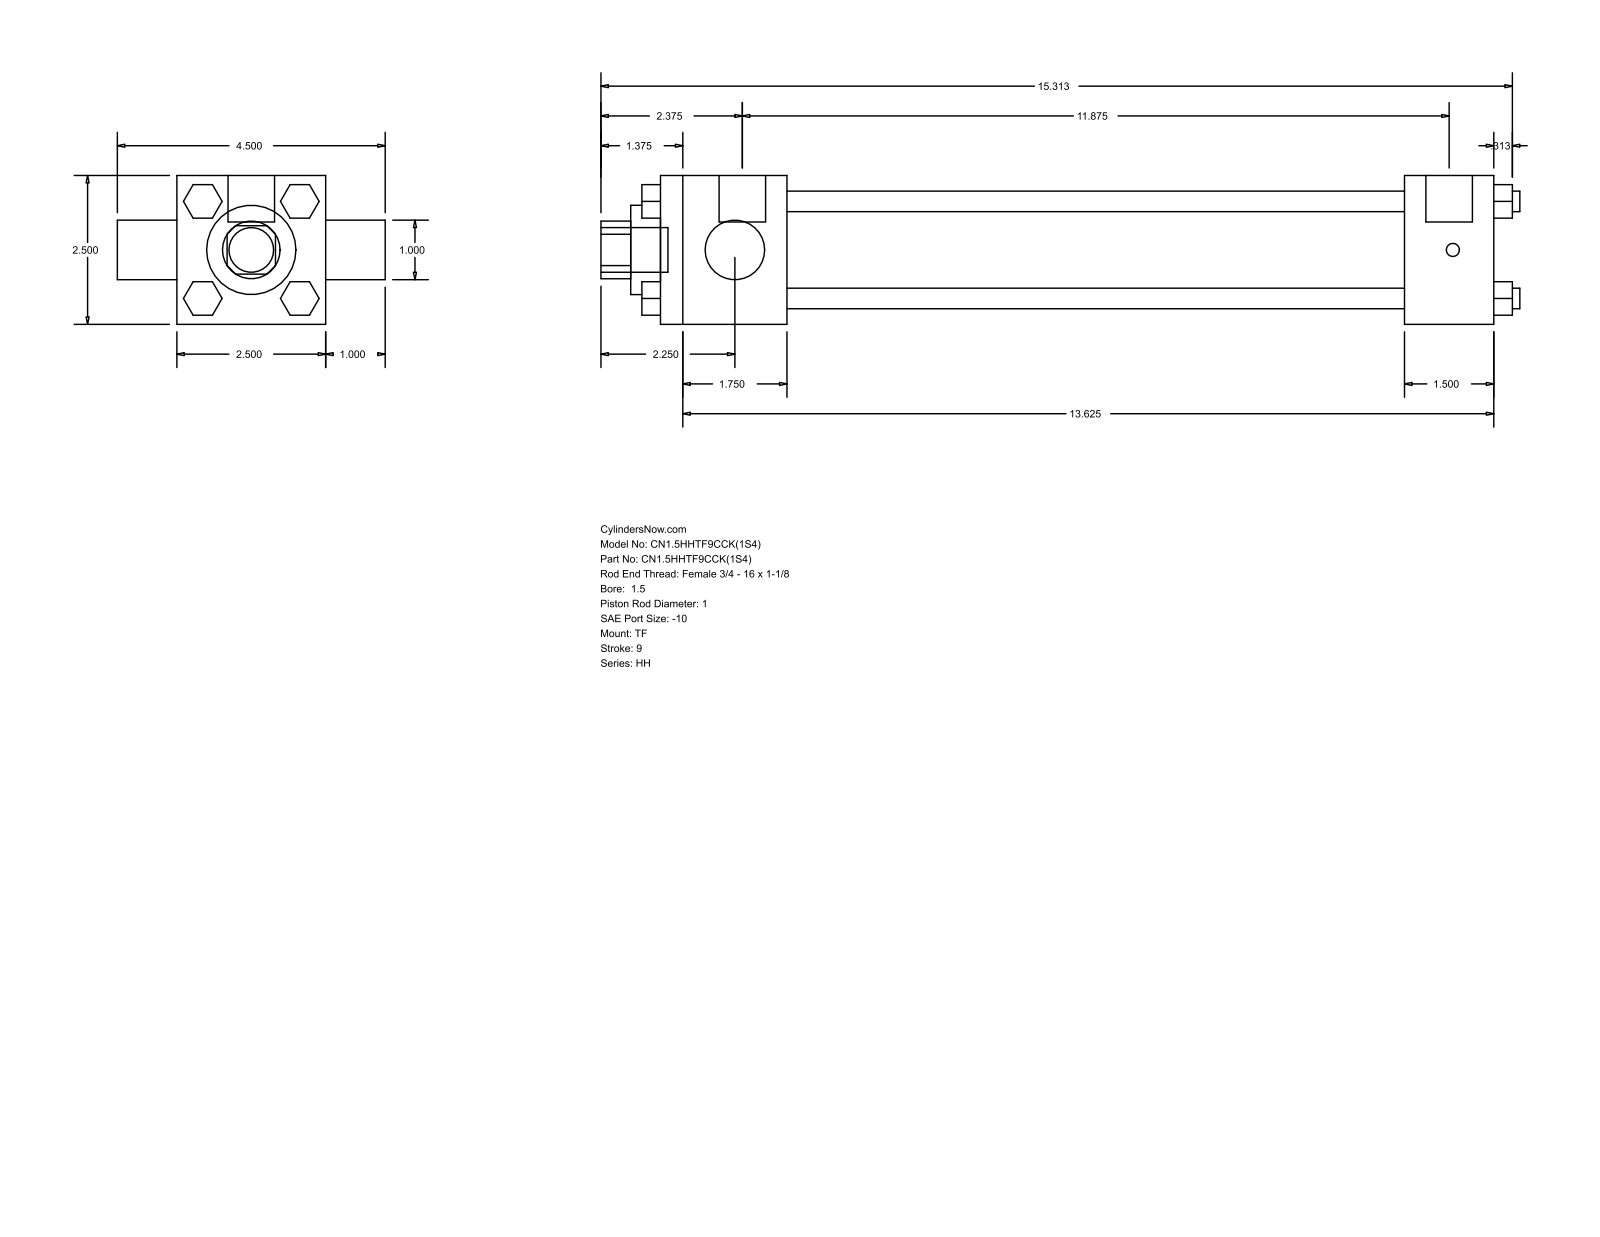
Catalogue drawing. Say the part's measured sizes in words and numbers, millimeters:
The part is named "HH_TF__0150_1". Its 3-D file was written by "GSSL Pune (CONFIG_CONTROL_DESIGN)". It is 0 solids with 120 faces: 92 planar, 28 cylindrical and 0 other. Overall it measures 392.11 by 114.3 by 63.5 millimeters. Round holes: 2 of diameter 25.4, 1 of diameter 38.1, 1 of diameter 44.45. Round bosses or shafts: 4 of diameter 8.76, 3 of diameter 5.56, 2 of diameter 19.84, 1 of diameter 19.05. Partial cylindrical surfaces (rounded edges, fillets, slot ends): 1 of radius 12.29. The main face-to-face distances are 63.5, 301.62, 263.52, 38.1, 53.98, 317.5, 355.6, 363.54, 25.4, 20.7.
